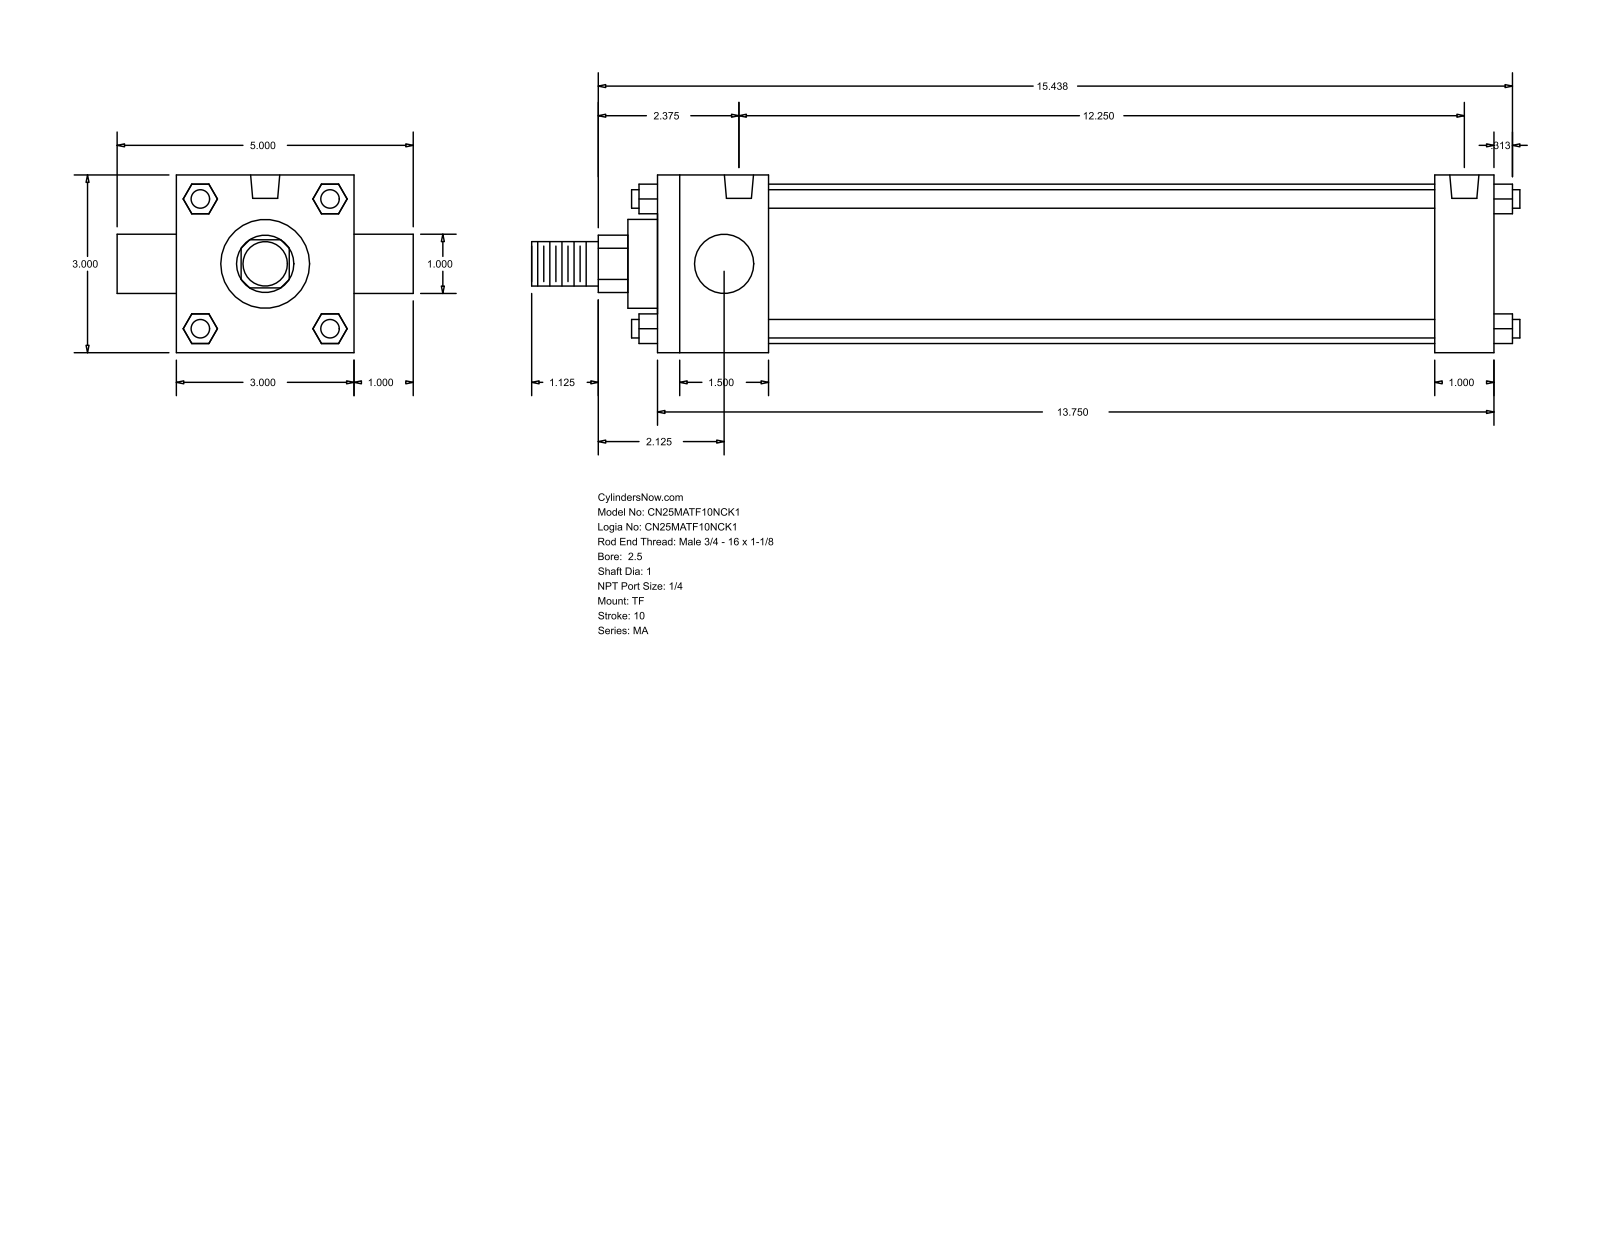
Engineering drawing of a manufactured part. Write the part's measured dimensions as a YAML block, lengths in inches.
part_name: "MA_TF__0250_1"
step_written_by: "GSSL Pune (CONFIG_CONTROL_DESIGN)"
units: inches
bodies: {solids: 0, faces: 120, planar: 92, cylindrical: 28, other: 0}
overall_size: [16.687, 5, 3]
round_holes:
  - {diameter: 0.313, count: 3}
  - {diameter: 0.492, count: 2}
round_bosses_or_shafts:
  - {diameter: 0.313, count: 4}
  - {diameter: 1, count: 2}
  - {diameter: 2.69, count: 1}
  - {diameter: 1.5, count: 1}
  - {diameter: 0.75, count: 1}
partial_cylinders:
  - {radius: 0.484, count: 1}
face_to_face_distances: [3, 14.125, 0.5, 1.875, 13.125, 11.25, 12.25, 1, 4, 1]
hole_center_spacings: [12.25]
